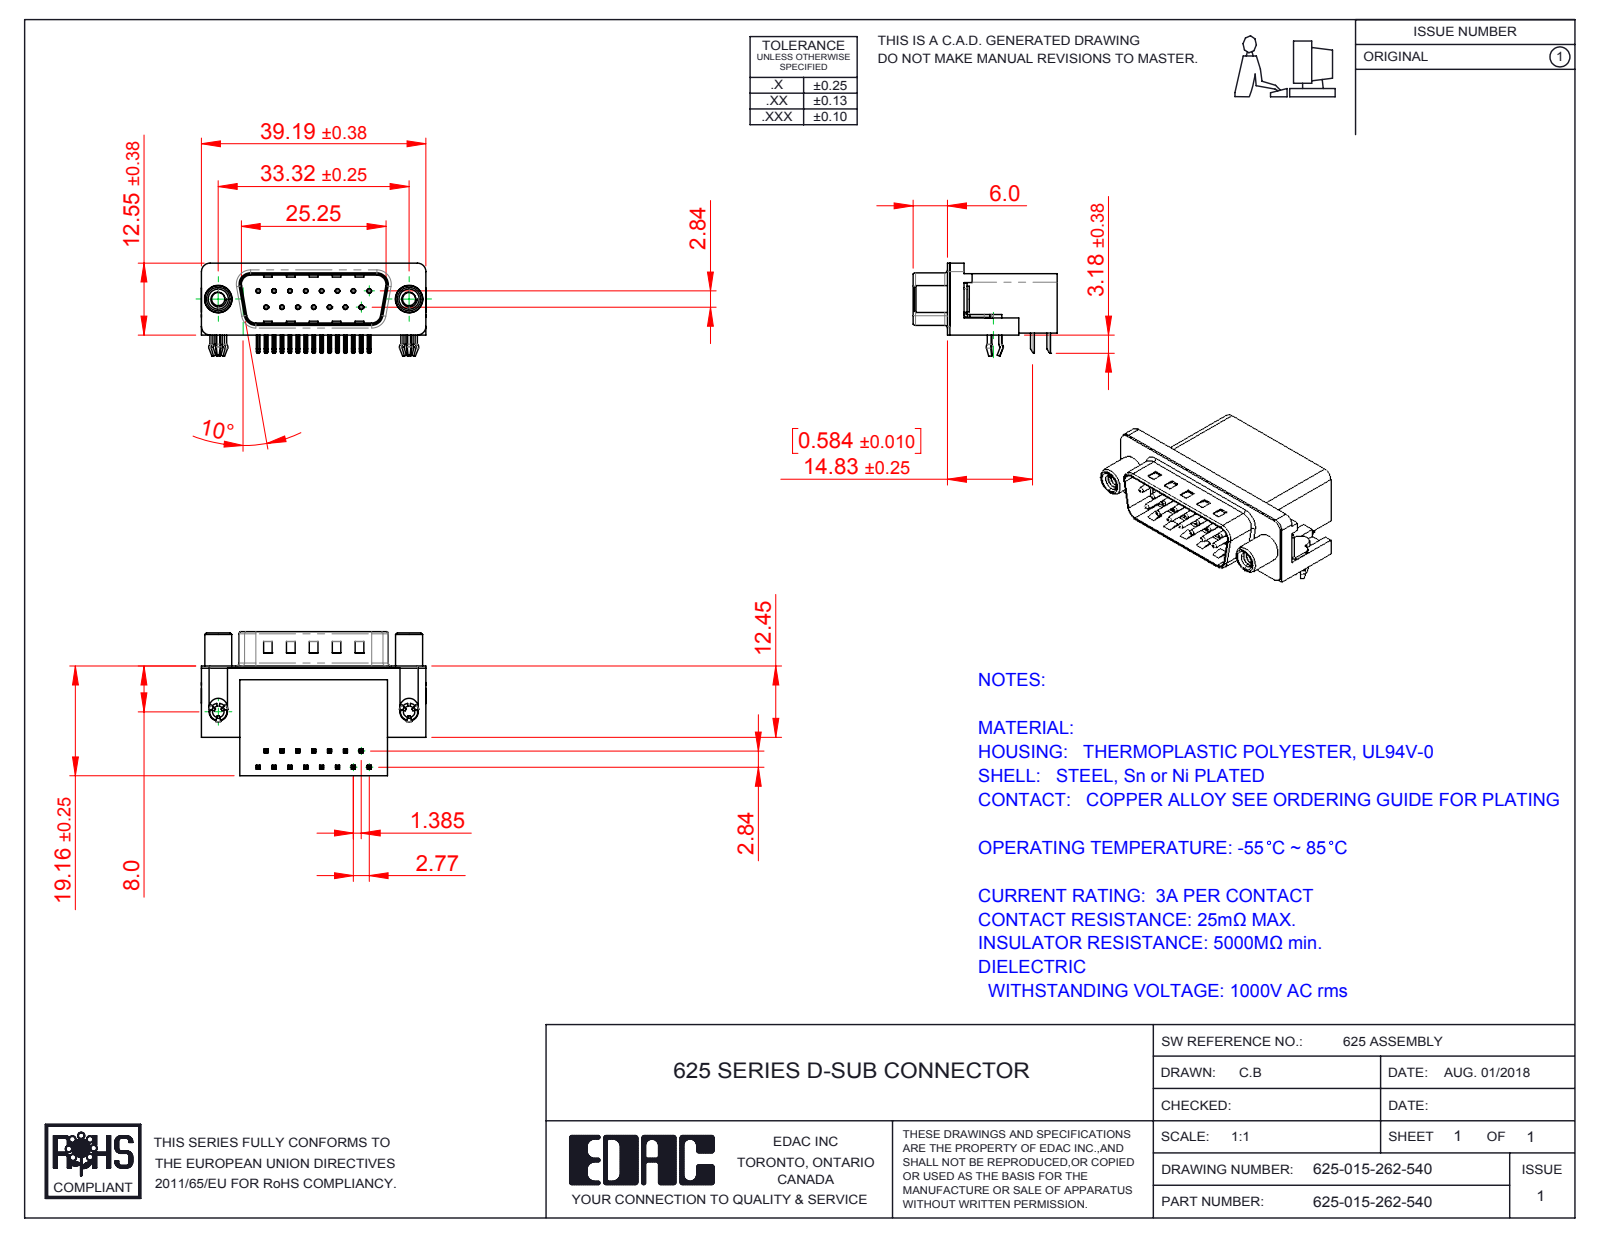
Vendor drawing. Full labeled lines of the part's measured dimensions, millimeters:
Part name (STEP PRODUCT): 625 3 Prong Board Lock; 625 Contact Top; 625 Round Threaded Standoff; 625 Contact Bottom (+3 more)
STEP written by: SolidWorks 2016 (CONFIG_CONTROL_DESIGN)
Units: millimetres
Bodies: 21 solids, 1577 faces (923 planar, 461 cylindrical, 193 other)
Overall size (bounding box): 39.22 × 25.16 × 16.25
Volume: 6 342 mm³ · Surface area: 6 685 mm²
Round holes (diameter × count): ⌀0.35 ×15, ⌀0.8 ×15, ⌀2 ×2, ⌀2.3 ×2, ⌀3.1 ×2, ⌀4 ×2, ⌀4.8 ×2, ⌀5 ×2
Round bosses / shafts (diameter × count): ⌀0.75 ×15, ⌀4.9 ×2, ⌀4.7 ×2, ⌀4.5 ×2, ⌀3.85 ×2, ⌀3 ×2
Partial cylindrical surfaces — rounded edges, fillets, slot ends (radius × count): R0.25 ×64, R0.12 ×30, R1 ×16, R0.5 ×9, R1.6 ×8, R1.5 ×6, R0.9 ×4, R2 ×4
Main face-to-face distances: 0.4, 10.35, 18.76, 2.1, 10.46, 1.7, 10.86, 19.16, 8.76, 16.26
Hole centre spacings: 3.16, 2.77, 5.54, 8.31, 11.08, 5.03, 5.04, 7.48
